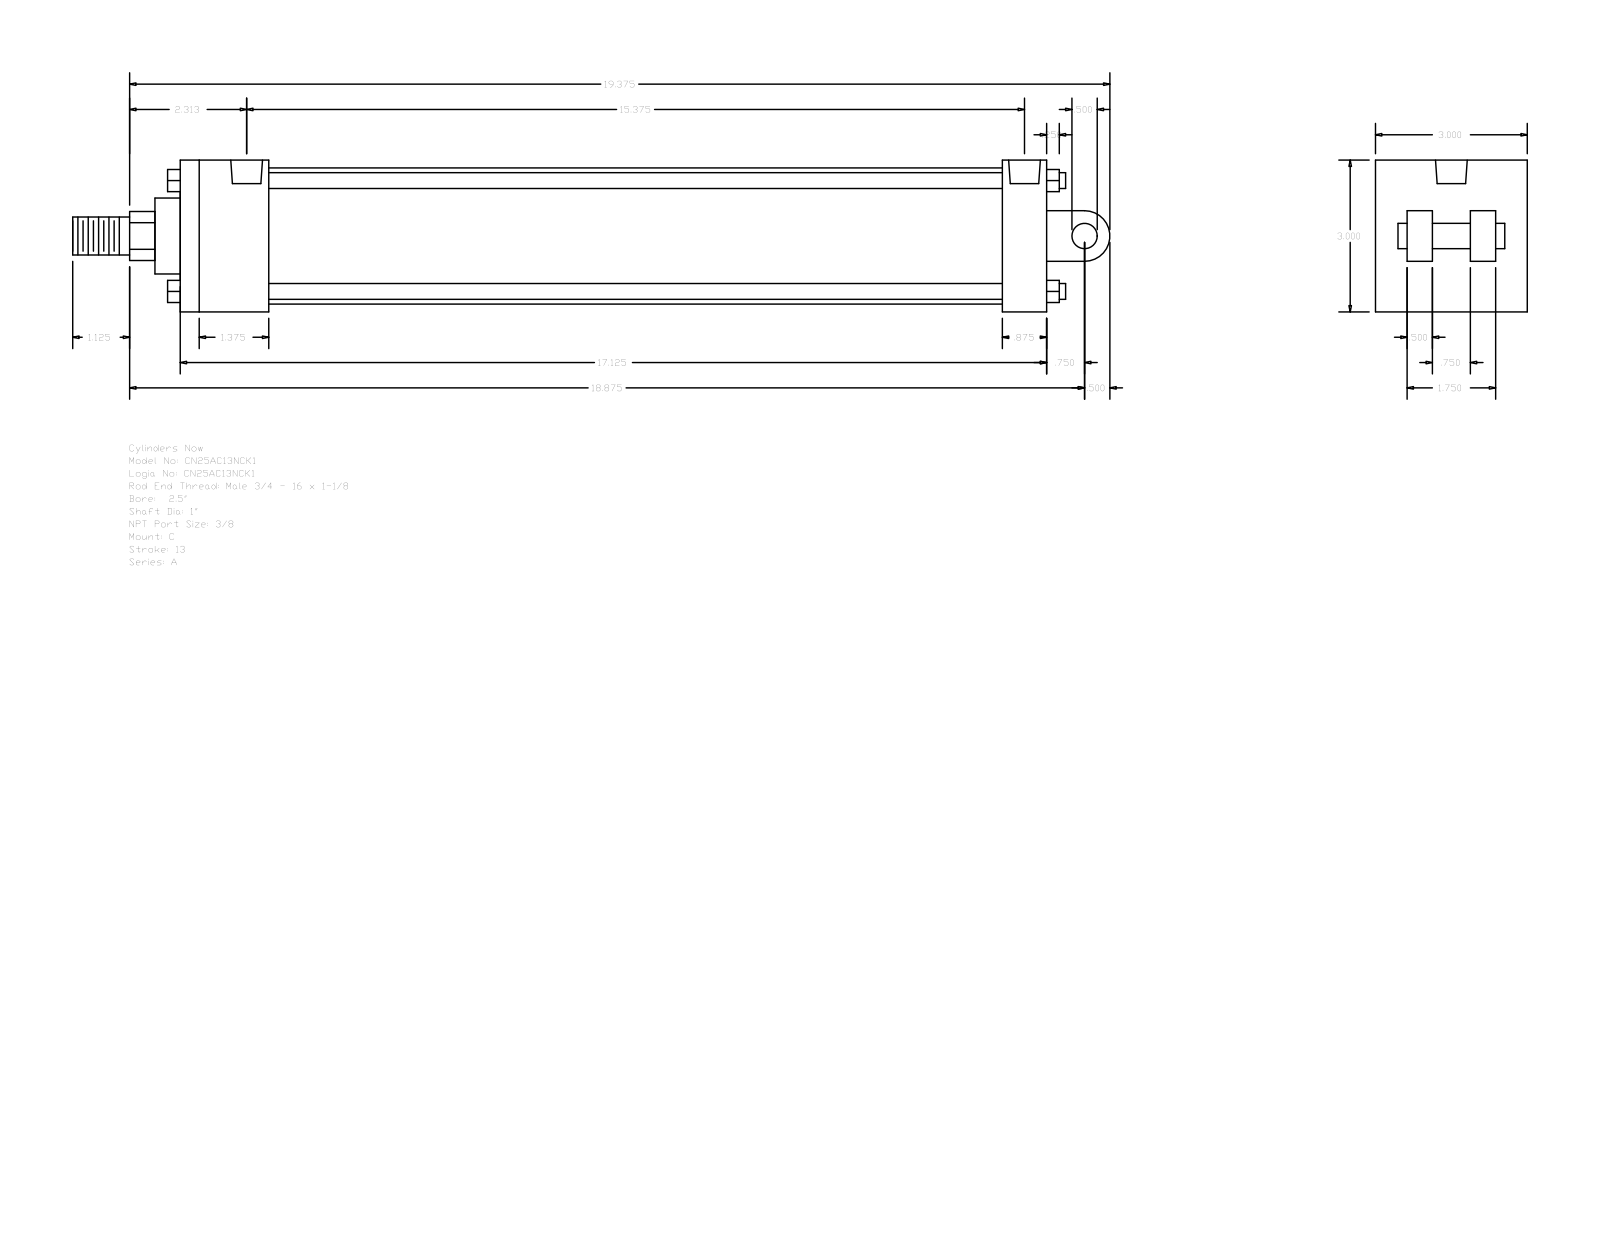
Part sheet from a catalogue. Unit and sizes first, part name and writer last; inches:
Units: inches
Overall size (bounding box): 20.5 × 3 × 3
Round holes (diameter × count): ⌀0.219 ×4, ⌀0.627 ×2
Round bosses / shafts (diameter × count): ⌀0.313 ×4, ⌀2.69 ×1, ⌀1.5 ×1, ⌀1 ×1, ⌀0.75 ×1, ⌀0.5 ×1
Partial cylindrical surfaces — rounded edges, fillets, slot ends (radius × count): R0.484 ×1, R0.5 ×1
Main face-to-face distances: 3, 17.125, 0.5, 1.75, 16.25, 14.5, 15.375, 0.875, 0.625, 1
Hole centre spacings: 0.094, 15.469, 15.562, 15.375
Bodies: 0 solids, 135 faces (102 planar, 33 cylindrical, 0 other)
Part name (STEP PRODUCT): A_C__0250_1
STEP written by: GSSL Pune (CONFIG_CONTROL_DESIGN)
